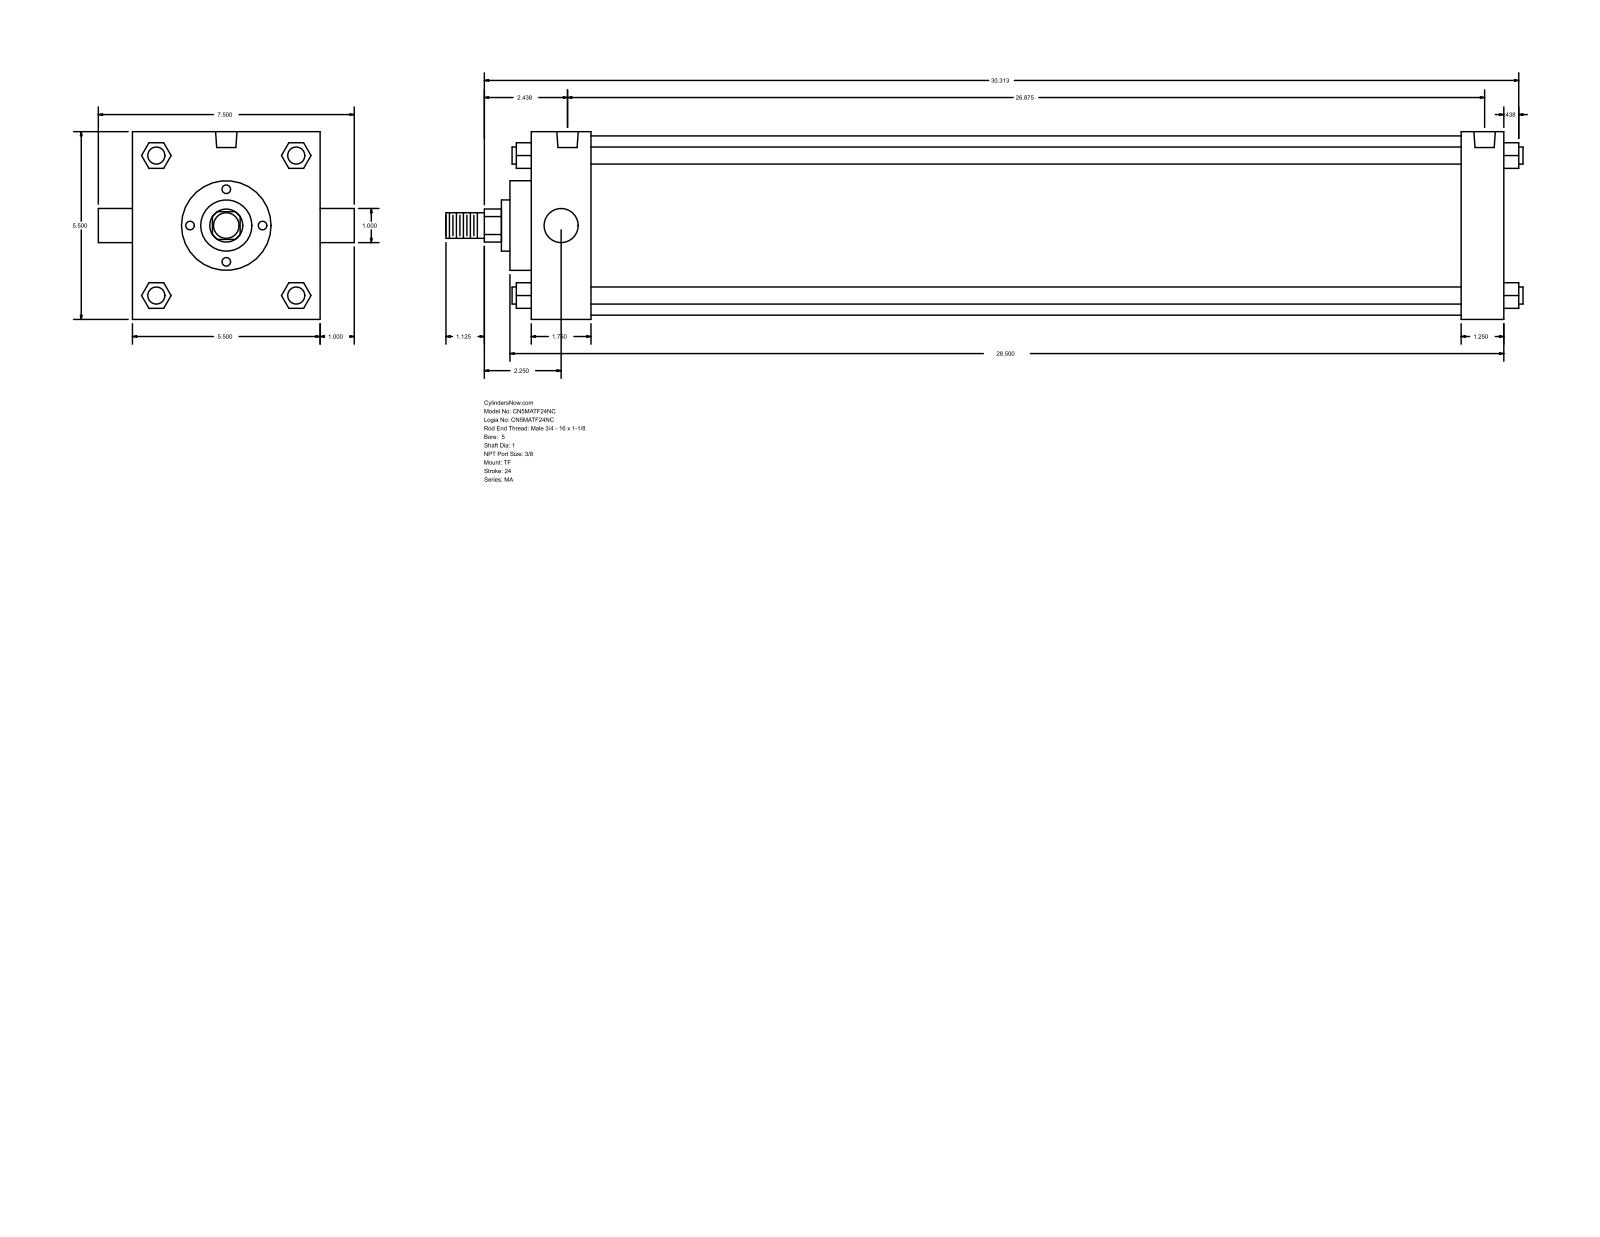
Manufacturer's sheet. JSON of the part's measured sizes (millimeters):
{"part_name": "MA_TF__0500_1", "step_written_by": "GSSL Pune (CONFIG_CONTROL_DESIGN)", "units": "millimeters", "bodies": {"solids": 0, "faces": 122, "planar": 93, "cylindrical": 29, "other": 0}, "overall_size": [801.69, 190.5, 139.7], "round_holes": [[11.11, 3], [15.93, 2]], "round_bosses_or_shafts": [[12.7, 4], [25.4, 2], [133.35, 1], [66.67, 1], [38.1, 1], [19.05, 1]], "partial_cylinders_radius": [[12.29, 1]], "face_to_face_distances": [139.7, 723.91, 692.16, 31.75, 44.46, 647.7, 679.45, 15.87, 60.33, 708.03], "hole_center_spacings": [4.76, 4.77, 673.1, 677.86, 677.87, 682.63]}
